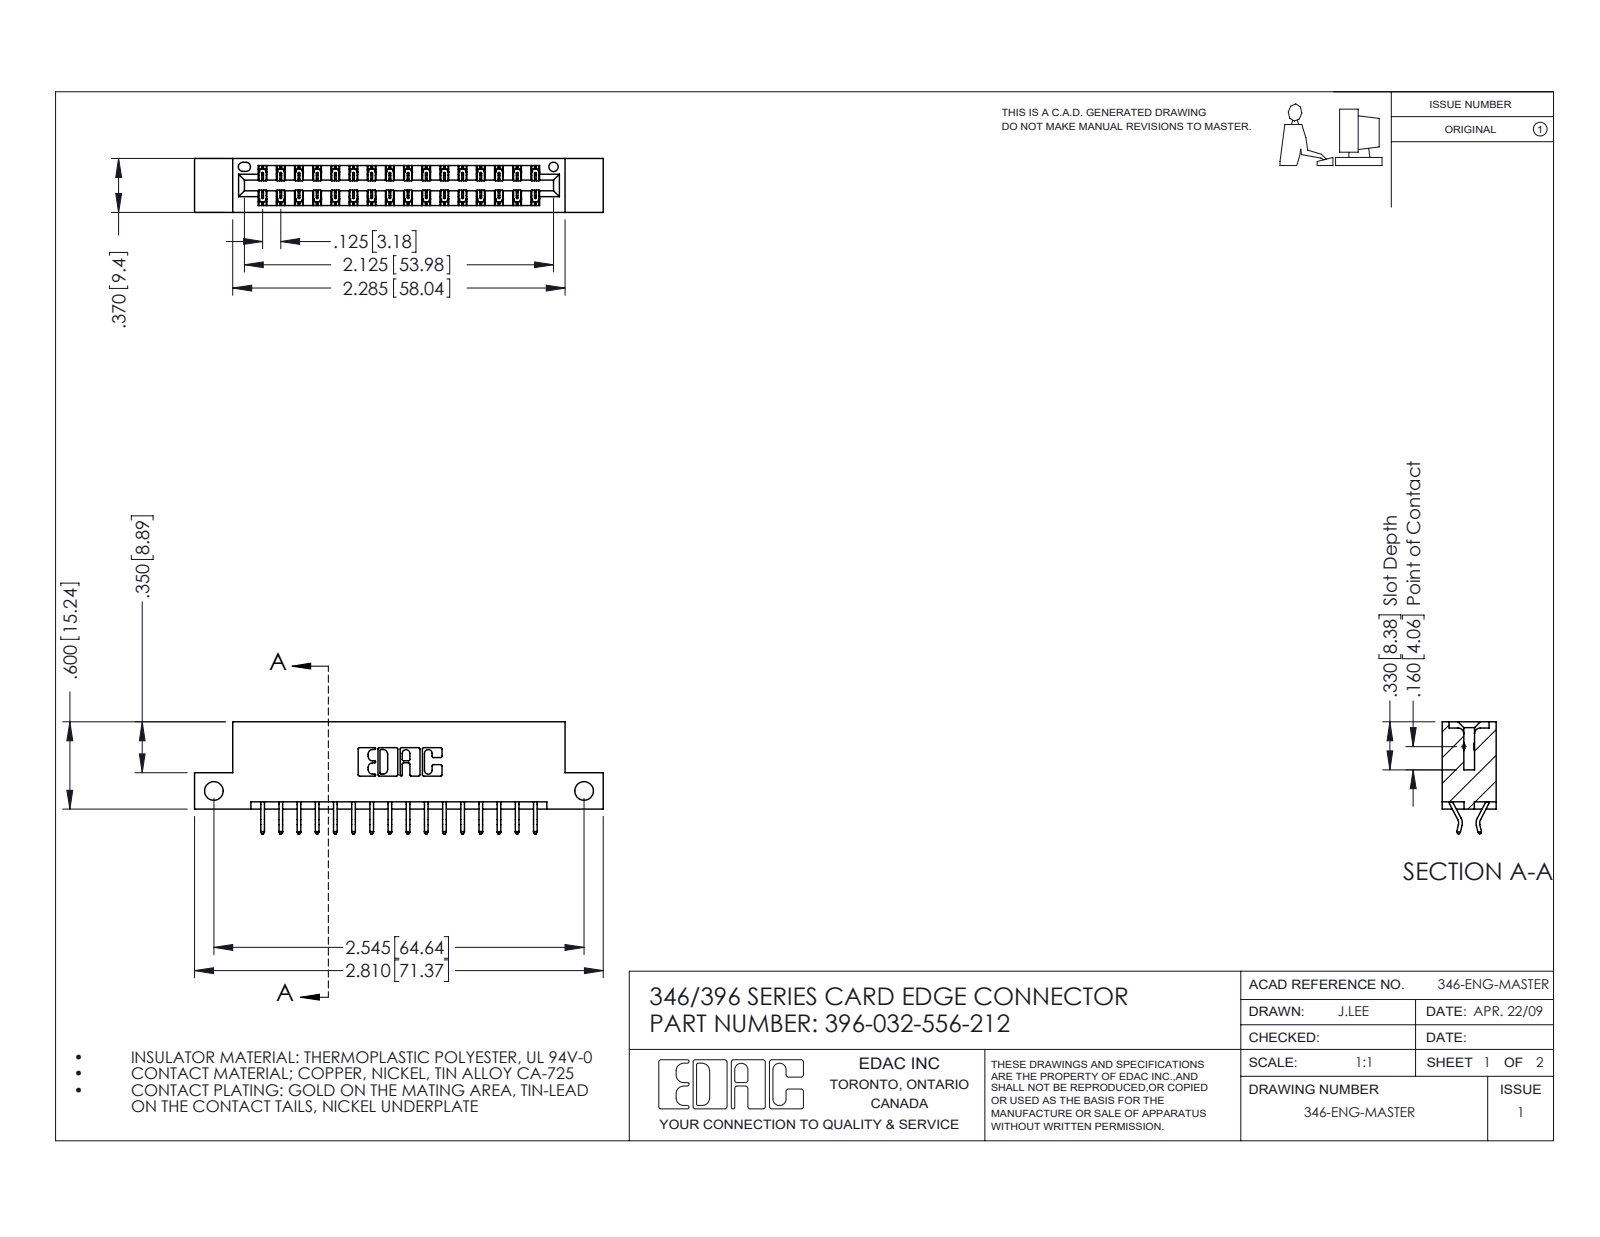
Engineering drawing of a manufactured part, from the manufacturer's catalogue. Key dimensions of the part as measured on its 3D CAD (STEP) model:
Part name (STEP PRODUCT): 345-292-001_556 Tail; 346 Part_Flush Mounting Lugs - Side Mount; 396-032-556-212
STEP written by: SolidWorks 2016 (CONFIG_CONTROL_DESIGN)
Units: inches
Bodies: 33 solids, 1978 faces (1324 planar, 654 cylindrical, 0 other)
Overall size (bounding box): 2.81 × 0.77 × 0.37
Volume: 0.407 in³ · Surface area: 13.32 in²
Round holes (diameter × count): ⌀0.128 ×2, ⌀0.064 ×1
Partial cylindrical surfaces — rounded edges, fillets, slot ends (radius × count): R0.006 ×48, R0.01 ×22, R0.007 ×6, R0.031 ×6, R0.026 ×3, R0.01 ×2, R0.014 ×2, R0.022 ×2
Main face-to-face distances: 0.048, 0.322, 0.25, 0.37, 0.025, 0.072, 0.298, 0.275, 0.148, 0.222
Hole centre spacings: 2.545
